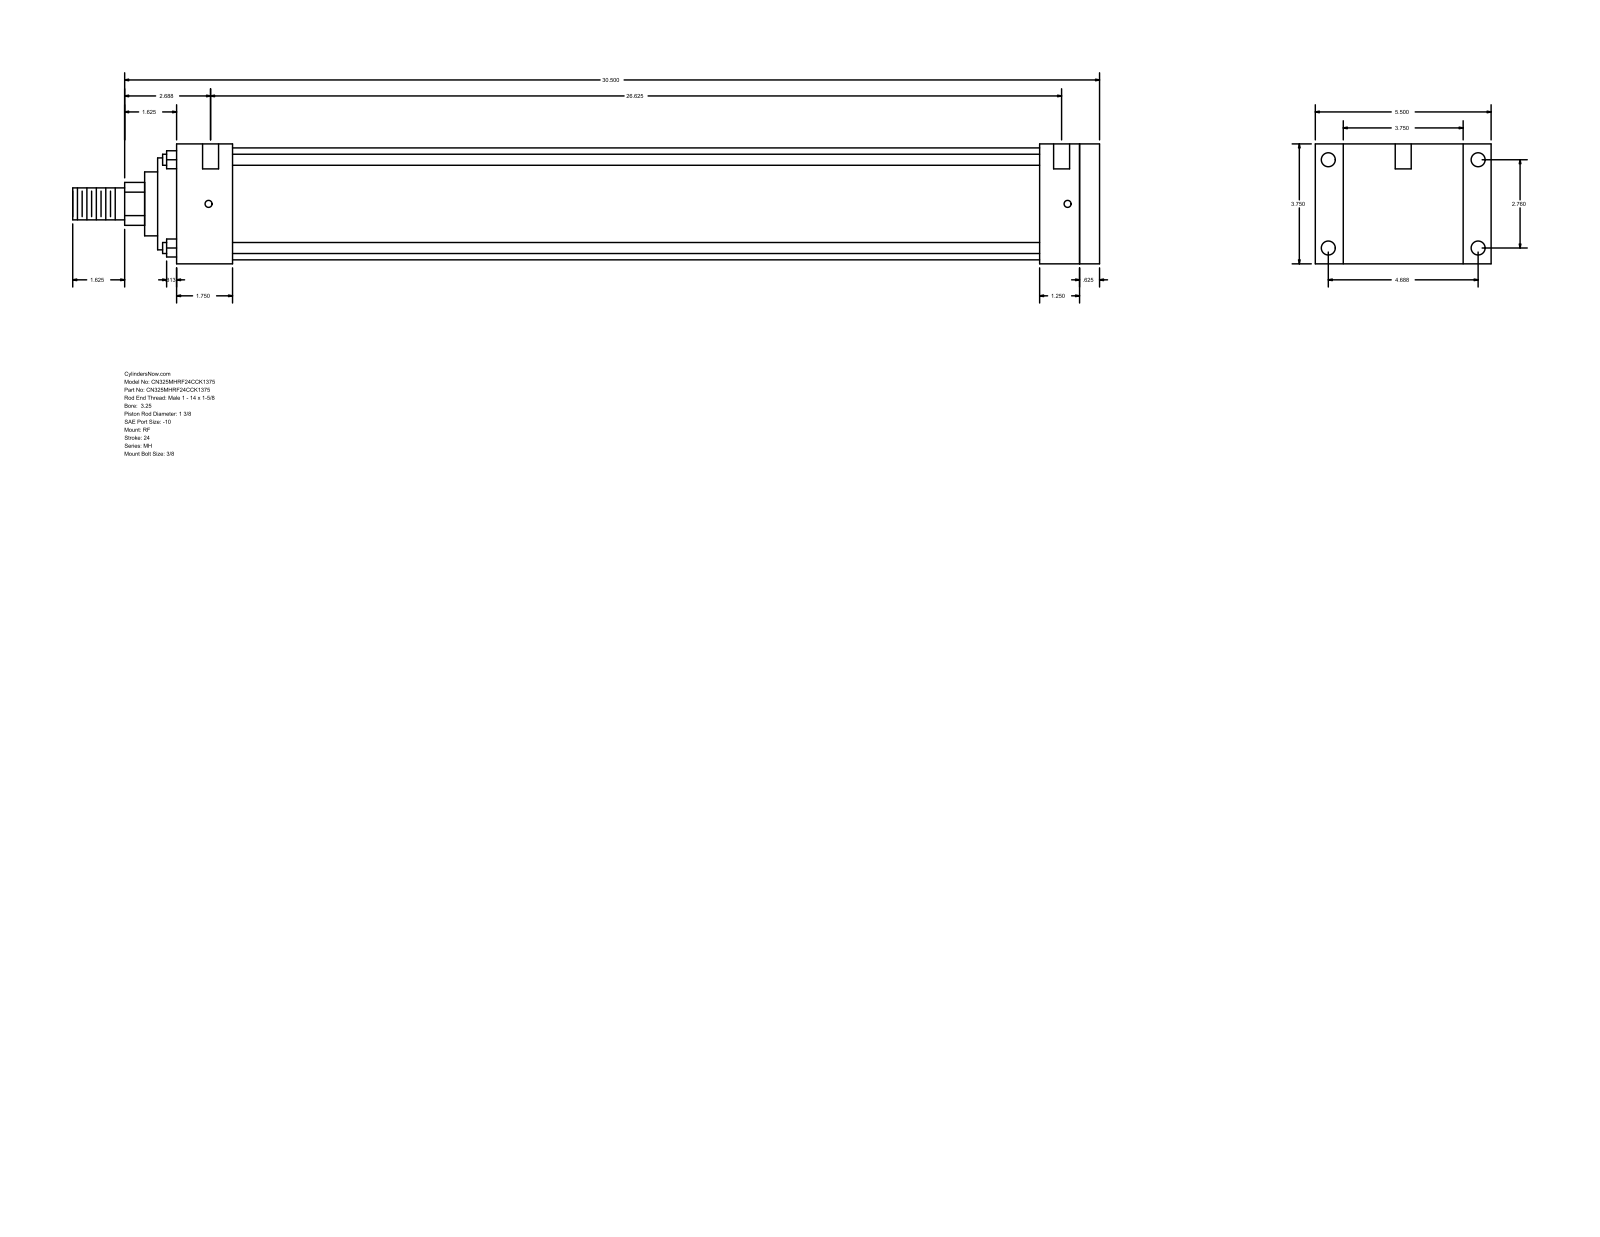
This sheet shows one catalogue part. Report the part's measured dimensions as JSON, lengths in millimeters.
{"part_name": "MH_RF__0325_1.375", "step_written_by": "GSSL Pune (CONFIG_CONTROL_DESIGN)", "units": "millimeters", "bodies": {"solids": 0, "faces": 94, "planar": 65, "cylindrical": 29, "other": 0}, "overall_size": [815.98, 139.7, 95.25], "round_holes": [[5.56, 4], [11.13, 4], [12.7, 2]], "round_bosses_or_shafts": [[8.76, 4], [88.9, 1], [73.03, 1], [50.8, 1], [34.92, 1], [25.4, 1]], "partial_cylinders_radius": [[17.06, 1]], "face_to_face_distances": [95.24, 733.43, 717.56, 15.87, 22.23, 117.47, 44.45, 673.11, 688.98, 685.81], "hole_center_spacings": [70.1, 119.06, 138.16, 682.63, 1.59, 4.76, 676.28, 677.87]}
